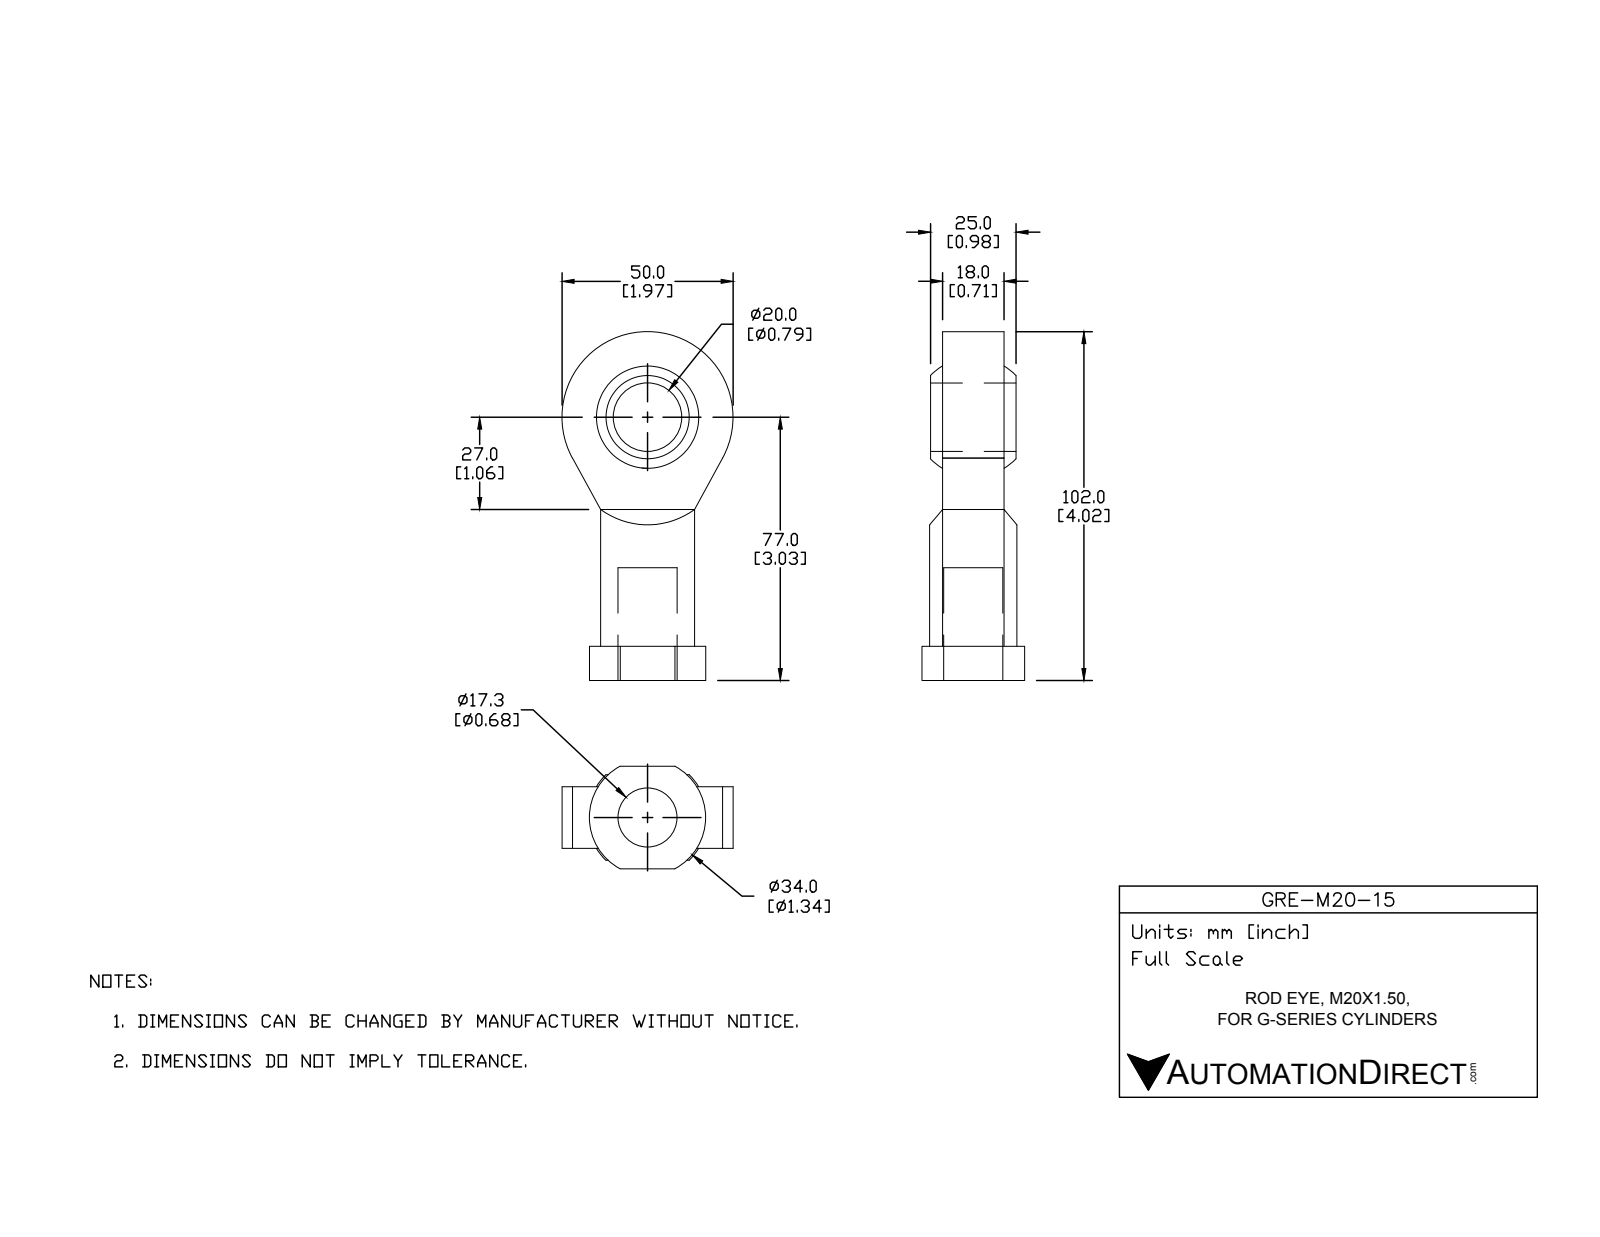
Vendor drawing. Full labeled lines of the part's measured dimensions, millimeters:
Part name (STEP PRODUCT): GRE-M20-15
STEP written by: SolidWorks 2017 (AUTOMOTIVE_DESIGN)
Units: millimetres
Bodies: 2 solids, 34 faces (12 planar, 16 cylindrical, 6 other)
Overall size (bounding box): 102 × 50 × 30
Volume: 53 796 mm³ · Surface area: 19 706 mm²
Round holes (diameter × count): ⌀18.5 ×1, ⌀20 ×1, ⌀30 ×1
Round bosses / shafts (diameter × count): ⌀29.9 ×1, ⌀27.5 ×1
Partial cylindrical surfaces — rounded edges, fillets, slot ends (radius × count): R17 ×1, R25 ×1
Main face-to-face distances: 18, 3.5, 21.5, 2.5, 6, 24, 27.5, 10, 25, 30
